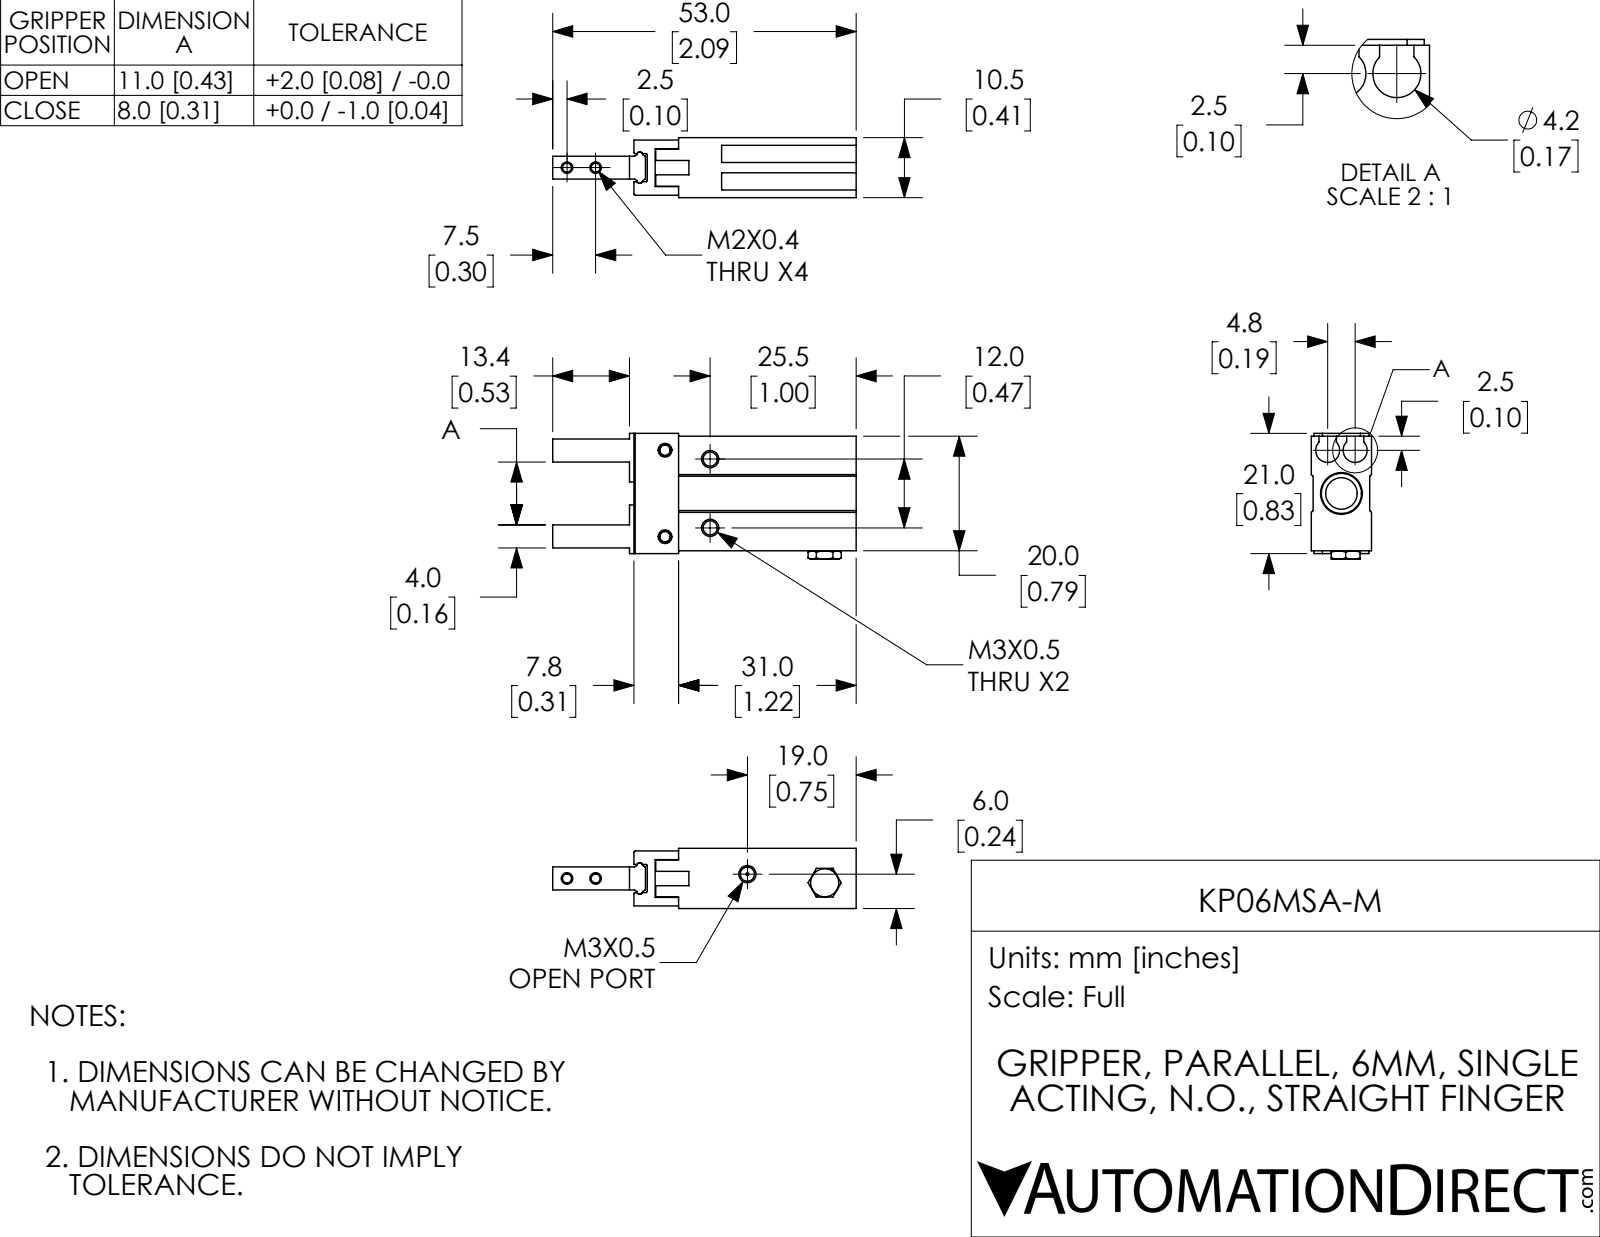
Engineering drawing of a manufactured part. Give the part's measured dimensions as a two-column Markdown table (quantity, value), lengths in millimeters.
| quantity | value |
| --- | --- |
| part name | KP06MSA-M-2; KP06MSA-M-3; KP06MSA-M; KP06MSA-M-1 |
| STEP written by | SolidWorks 2017 (CONFIG_CONTROL_DESIGN) |
| units | millimeters |
| bodies | 3 solids, 196 faces (102 planar, 44 cylindrical, 50 other) |
| overall size | 53 × 22 × 10.5 |
| volume | 7 053 mm³ |
| surface area | 5 221 mm² |
| round holes (diameter × count) | 2.46 × 3, 0.5 × 2, 1.57 × 2, 3.1 × 2, 2.46 × 1, 5.5 × 1, 7 × 1 |
| partial cylindrical surfaces (radius × count) | 0.2 × 4, 0.5 × 2, 2.1 × 2 |
| main face-to-face distances | 4, 3.25, 2, 10.5, 10.2, 3.7, 0.45, 2.8, 6.5, 10.05 |
| hole center spacings | 5, 12, 13.58, 26.51, 31.51, 40.01, 45.01 |
